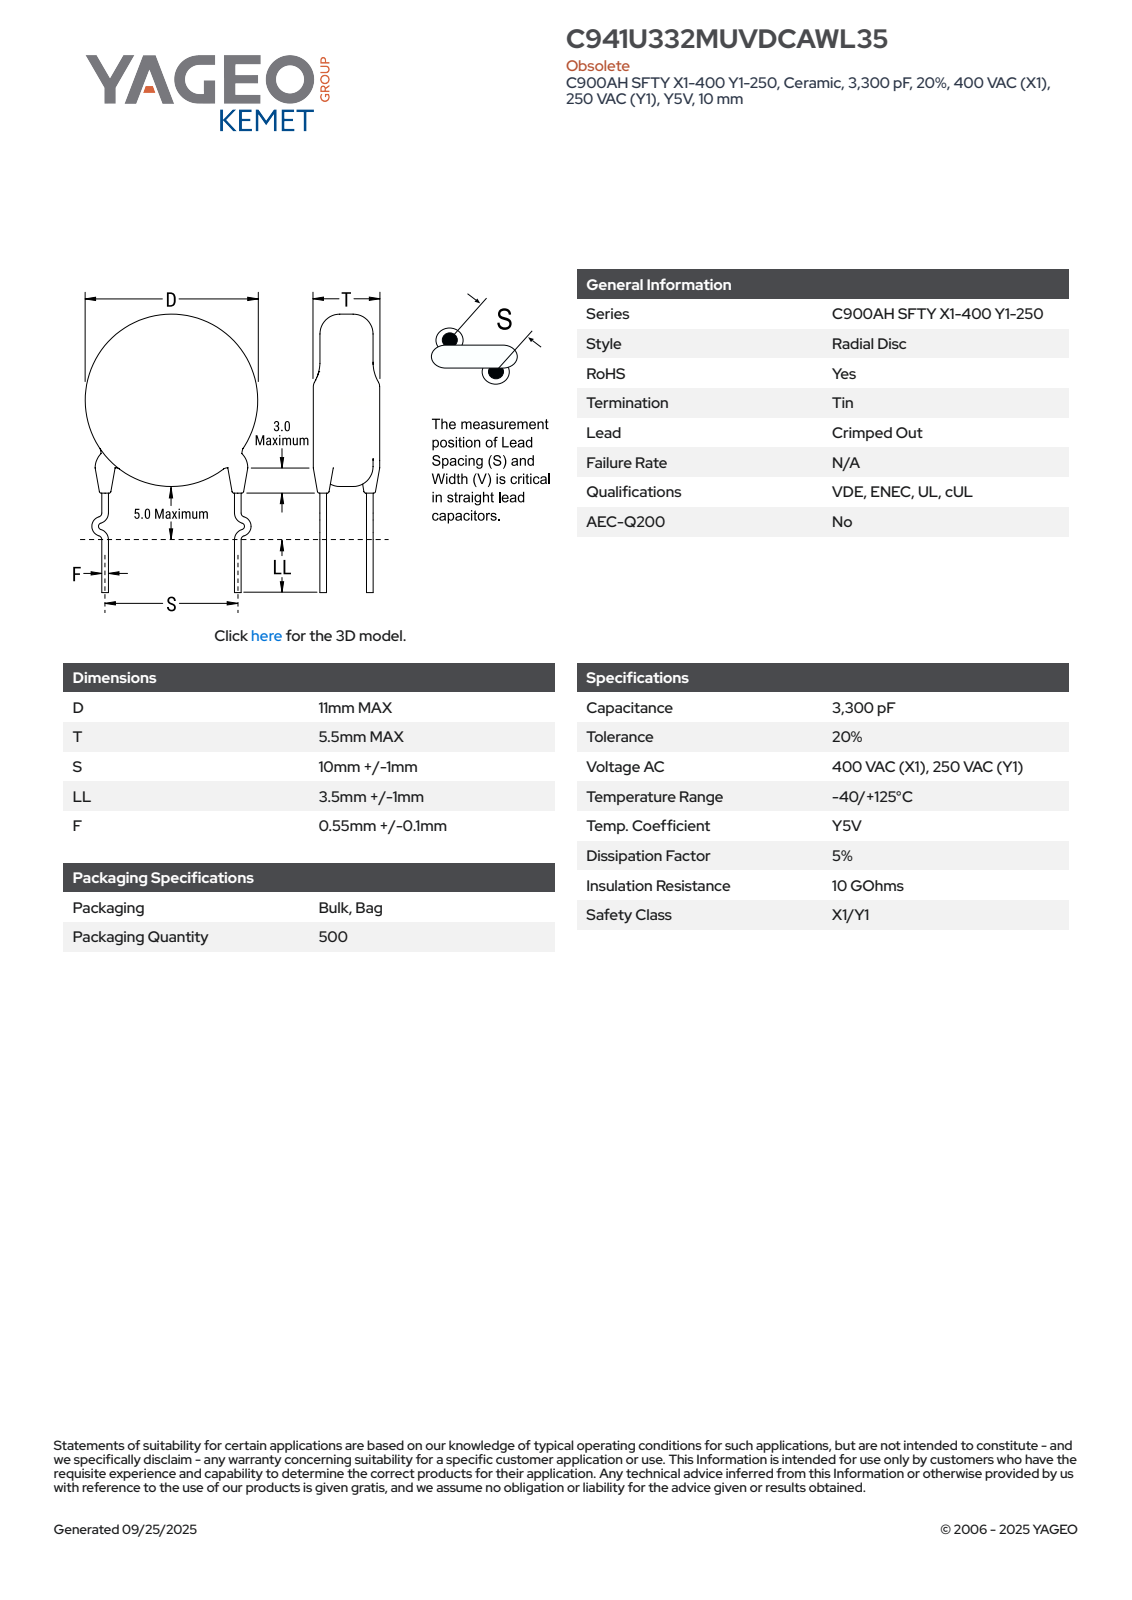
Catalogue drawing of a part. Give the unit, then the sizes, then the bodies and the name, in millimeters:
Units: millimetres
Overall size (bounding box): 20.5 × 14.69 × 5.5
Round bosses / shafts (diameter × count): ⌀1.2 ×2, ⌀11 ×1
Main face-to-face distances: 5.5, 1.14, 6.08, 4.94, 0.32, 0.92, 4.67, 2.36, 3.39, 3.53
Volume: 523 mm³ · Surface area: 426 mm²
Bodies: 4 solids, 87 faces (63 planar, 6 cylindrical, 18 other)
Part name (STEP PRODUCT): CCD_KCOC900_D11T5.5S10LL4.5F0.55
STEP written by: SolidWorks 2014 (AUTOMOTIVE_DESIGN)
